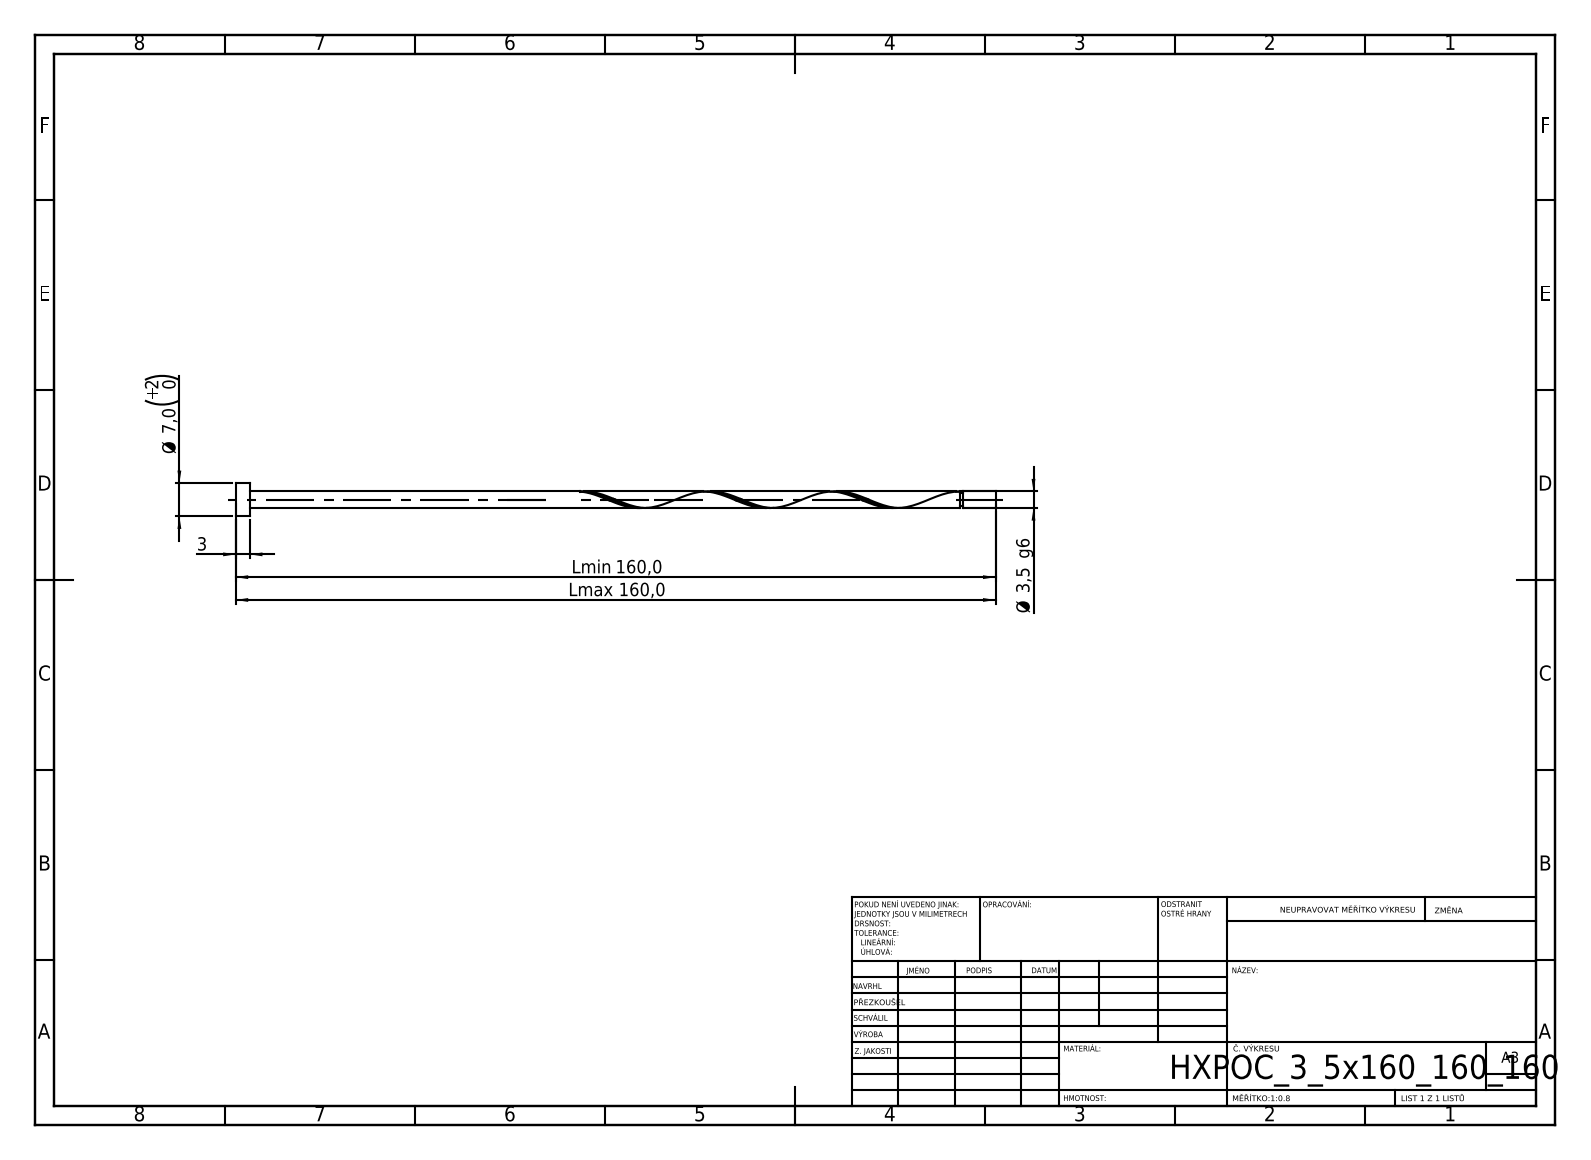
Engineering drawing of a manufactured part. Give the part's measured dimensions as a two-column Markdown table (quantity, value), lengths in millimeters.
| quantity | value |
| --- | --- |
| STEP written by | SolidWorks 2019 (CONFIG_CONTROL_DESIGN) |
| units | millimeters |
| bodies | 1 solid, 21 faces (6 planar, 14 cylindrical, 1 other) |
| overall size | 160 × 7 × 7 |
| volume | 1 609 mm³ |
| surface area | 1 904 mm² |
| round bosses / shafts (diameter × count) | 7 × 1, 3.5 × 1, 2.8 × 1 |
| main face-to-face distances | 3, 160, 157, 153.23, 150.23, 6.77, 152.53, 149.53, 0.7, 7.47 |
